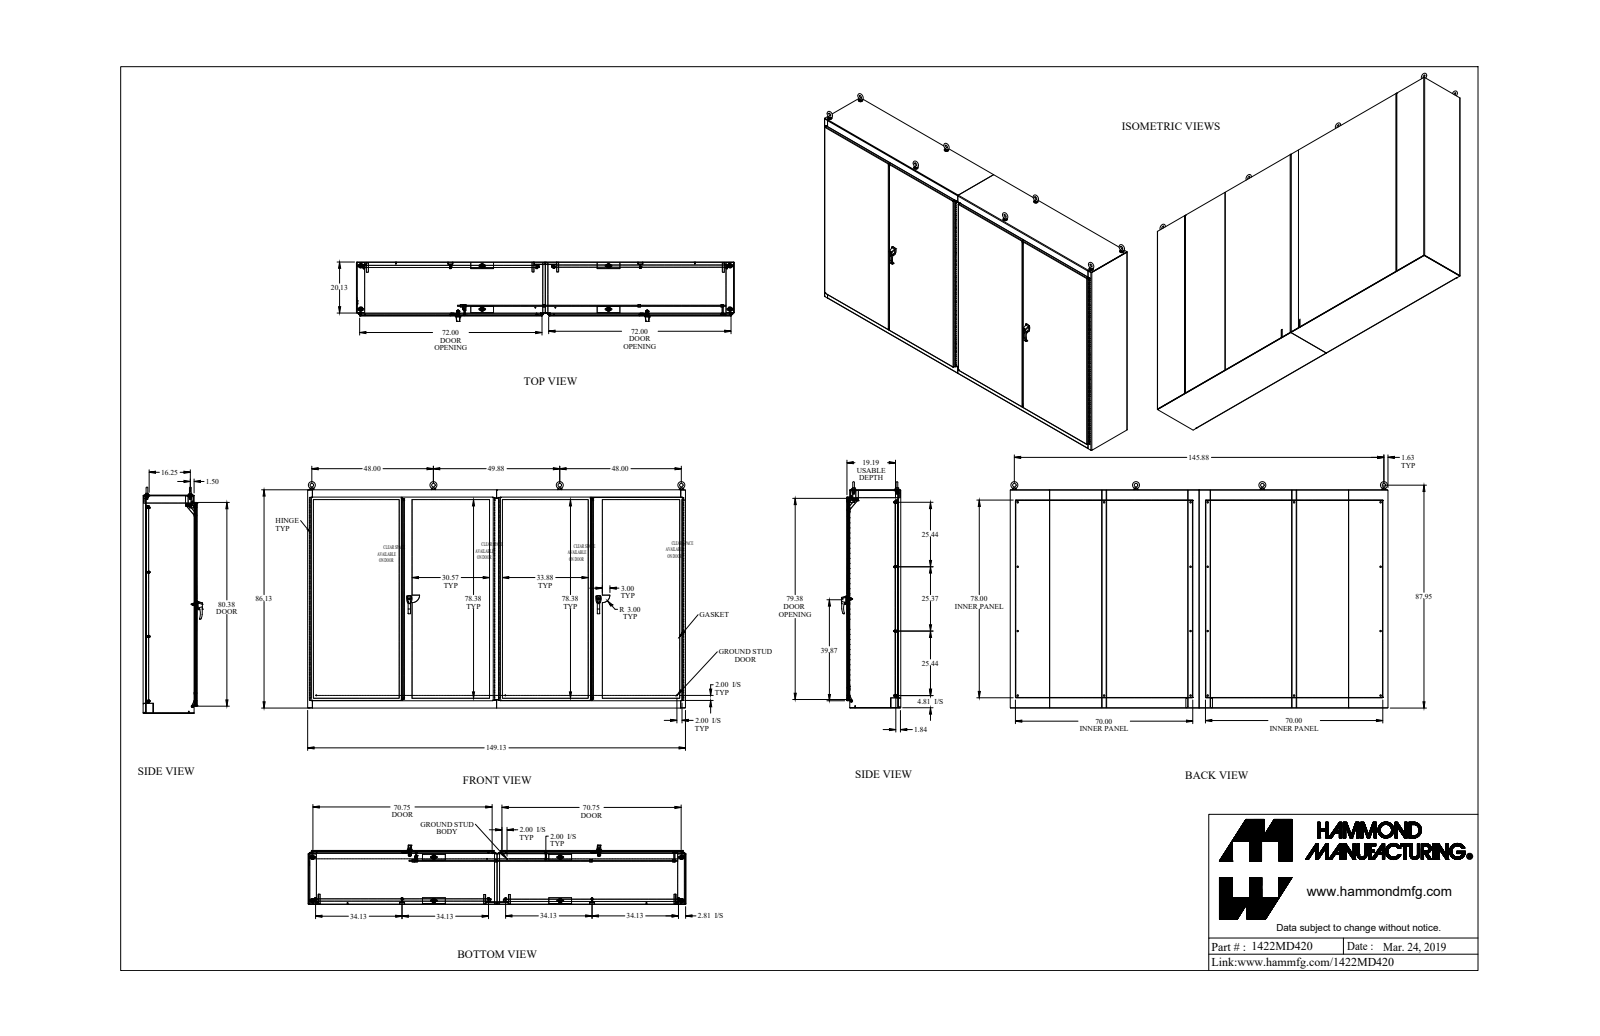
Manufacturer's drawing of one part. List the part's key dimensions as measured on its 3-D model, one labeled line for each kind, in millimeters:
Part name (STEP PRODUCT): 1422MD420_Default
STEP written by: SolidWorks 2019 (CONFIG_CONTROL_DESIGN)
Units: millimetres
Bodies: 223 solids, 6547 faces (2871 planar, 3037 cylindrical, 639 other)
Overall size (bounding box): 3787.8 × 2280.4 × 594.4
Volume: 111 500 000 mm³ · Surface area: 69 050 000 mm²
Round holes (diameter × count): ⌀7.7 ×56, ⌀7.8 ×20, ⌀14.3 ×20, ⌀11.3 ×12, ⌀11.3 ×8, ⌀13.4 ×8, ⌀17.4 ×8, ⌀17.4 ×8, ⌀7.1 ×6, ⌀9.9 ×5, ⌀2.8 ×4, ⌀8 ×4
Round bosses / shafts (diameter × count): ⌀25.4 ×23, ⌀9.5 ×21, ⌀16.5 ×20, ⌀8.4 ×20, ⌀7.1 ×11, ⌀44.5 ×8, ⌀38.1 ×8, ⌀31.8 ×8
Partial cylindrical surfaces — rounded edges, fillets, slot ends (radius × count): R1.5 ×71, R4.7 ×62, R0.4 ×32, R3.2 ×31, R1.3 ×16, R0.8 ×12, R2.3 ×12, R8.1 ×10
Main face-to-face distances: 3.2, 537.5, 485.1, 52.4, 534.3, 540.7, 482, 55.5, 488.3, 49.2
Hole centre spacings: 1905, 152.4, 304.8, 866.8, 1081.1, 1554.7, 1733.6, 2011.6
